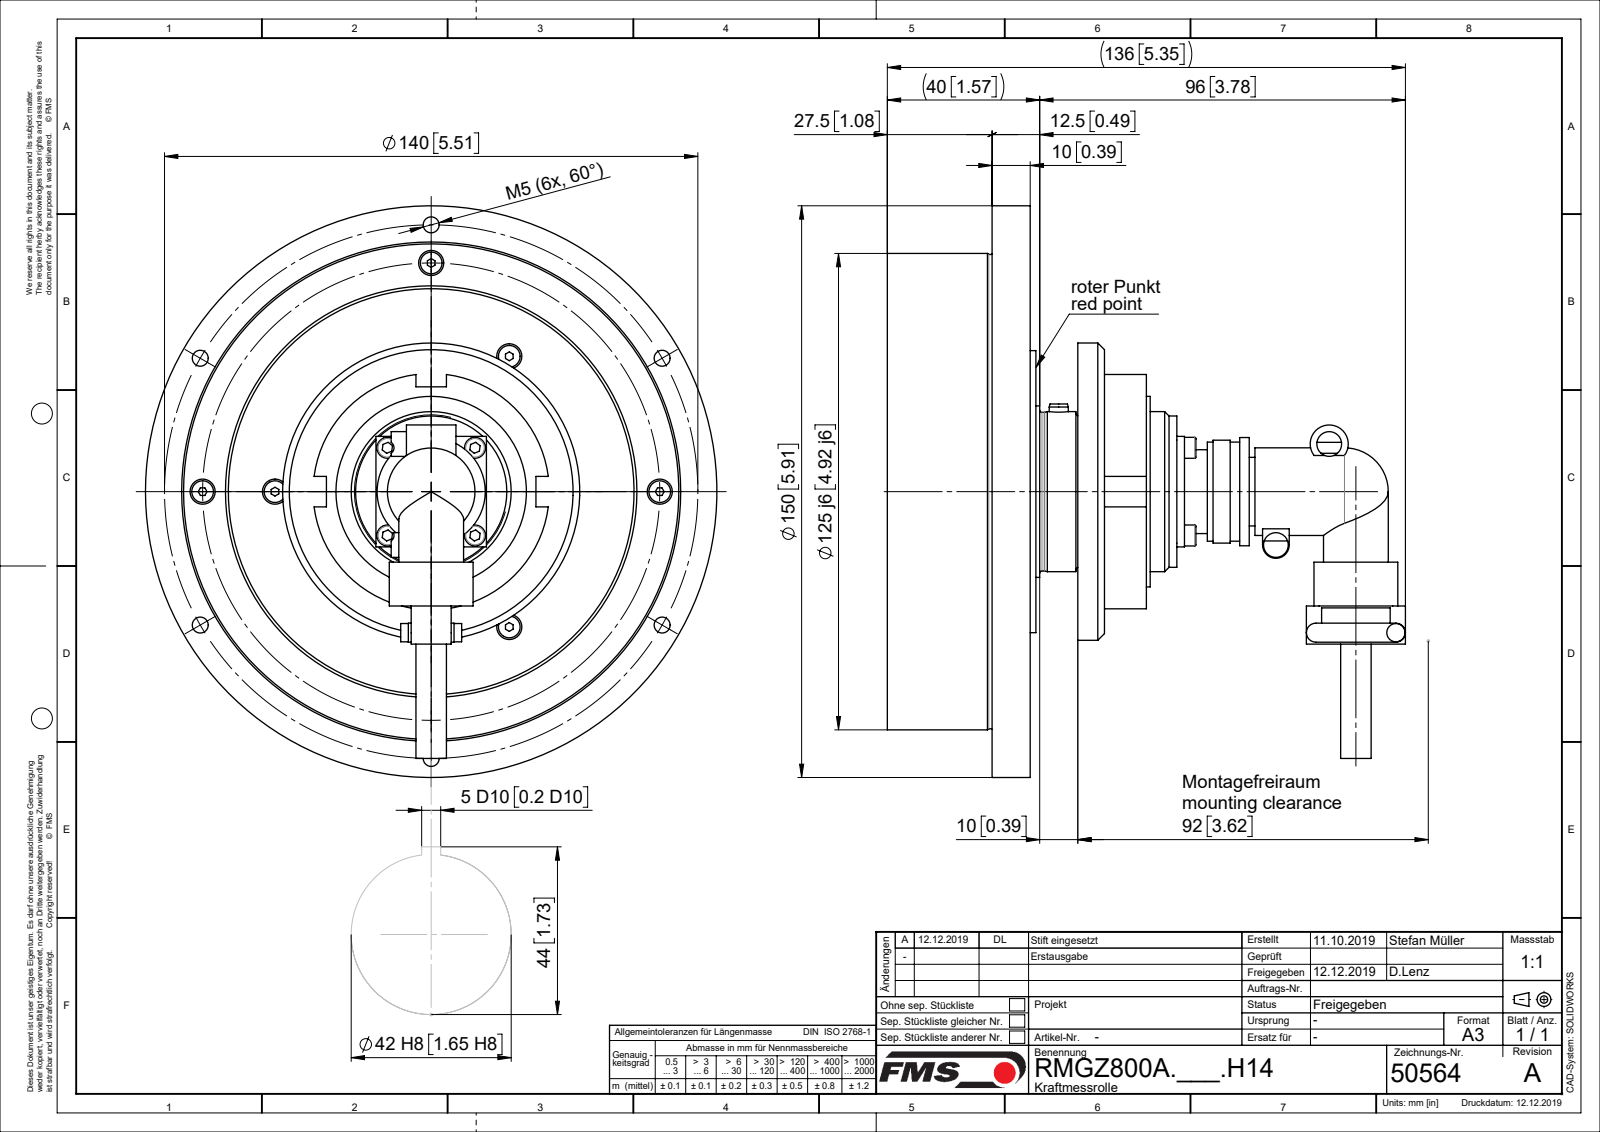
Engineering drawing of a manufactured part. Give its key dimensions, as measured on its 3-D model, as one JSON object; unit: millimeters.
{"part_name": "R50564; R4753004; TEIL1; R47533 (+8 more)", "step_written_by": "Mechanical Desktop 2009 (CONFIG_CONTROL_DESIGN)", "units": "millimeters", "bodies": {"solids": 18, "faces": 444, "planar": 137, "cylindrical": 200, "other": 107}, "overall_size": [150, 150, 136], "volume_mm3": 600565, "surface_area_mm2": 190337, "round_holes": [[2.6, 7], [4.33, 6], [2.2, 4], [3.5, 4], [3.4, 3], [4, 1], [5, 1], [16, 1], [23, 1], [32.2, 1], [37.8, 1], [43, 1]], "round_bosses_or_shafts": [[3, 7], [5.5, 4], [6, 3], [22, 2], [6.5, 2], [4.8, 2], [150, 1], [125, 1]], "partial_cylinders_radius": [[2.5, 2], [3.5, 1], [5, 1]], "face_to_face_distances": [2, 4, 32, 35.5, 3.5, 15, 30, 37.5, 13, 28], "hole_center_spacings": [70, 47.42, 69.95, 121.24, 40.12, 81.12, 16.26, 23]}
